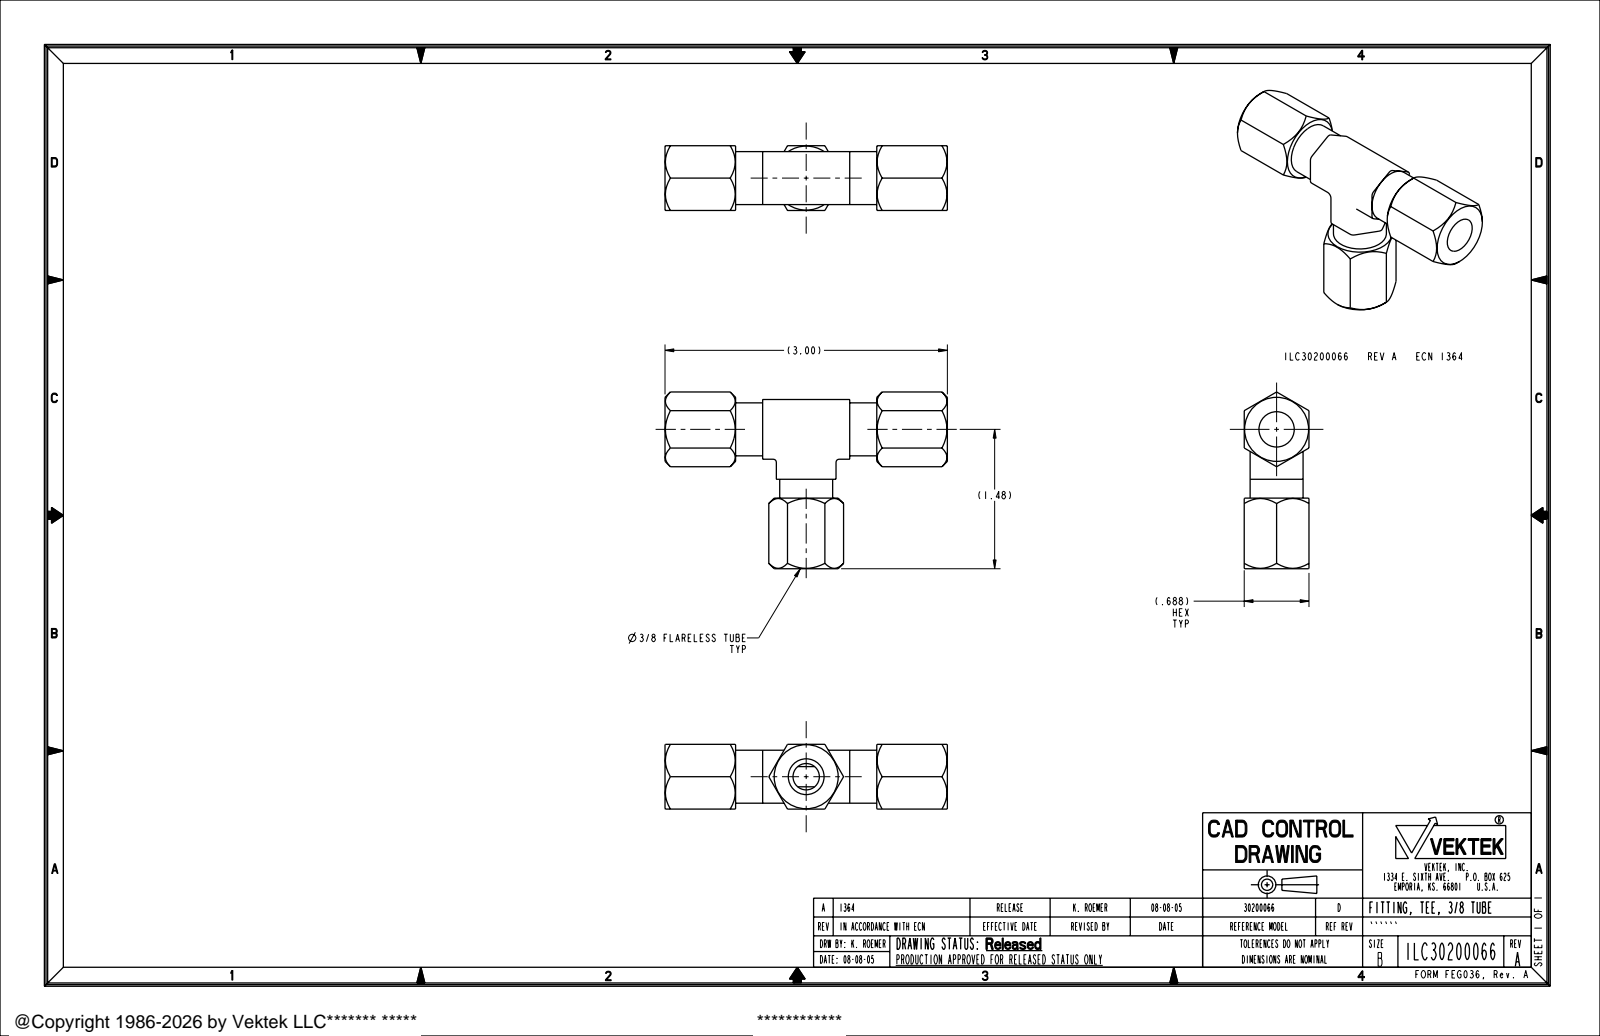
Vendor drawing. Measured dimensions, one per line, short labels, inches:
name: ILC30200066
written by: PRO/ENGINEER BY PARAMETRIC TECHNOLOGY CORPORATION, 2004290 (AUTOMOTIVE_DESIGN_CC2)
unit: in
bodies: 1 solid, 115 faces (60 planar, 37 cylindrical, 18 other)
size: 3 × 1.795 × 1.433
volume: 1.061 in³; area: 14.75 in²
holes: 2× ⌀0.28, 1× ⌀0.375, 1× ⌀0.38
bosses: 2× ⌀0.563
rounds: 16× R0.05
face distances: 0.687, 0.625, 0.063, 0.688, 0.063, 0.625, 0.562, 0.688, 0.75, 2.25
